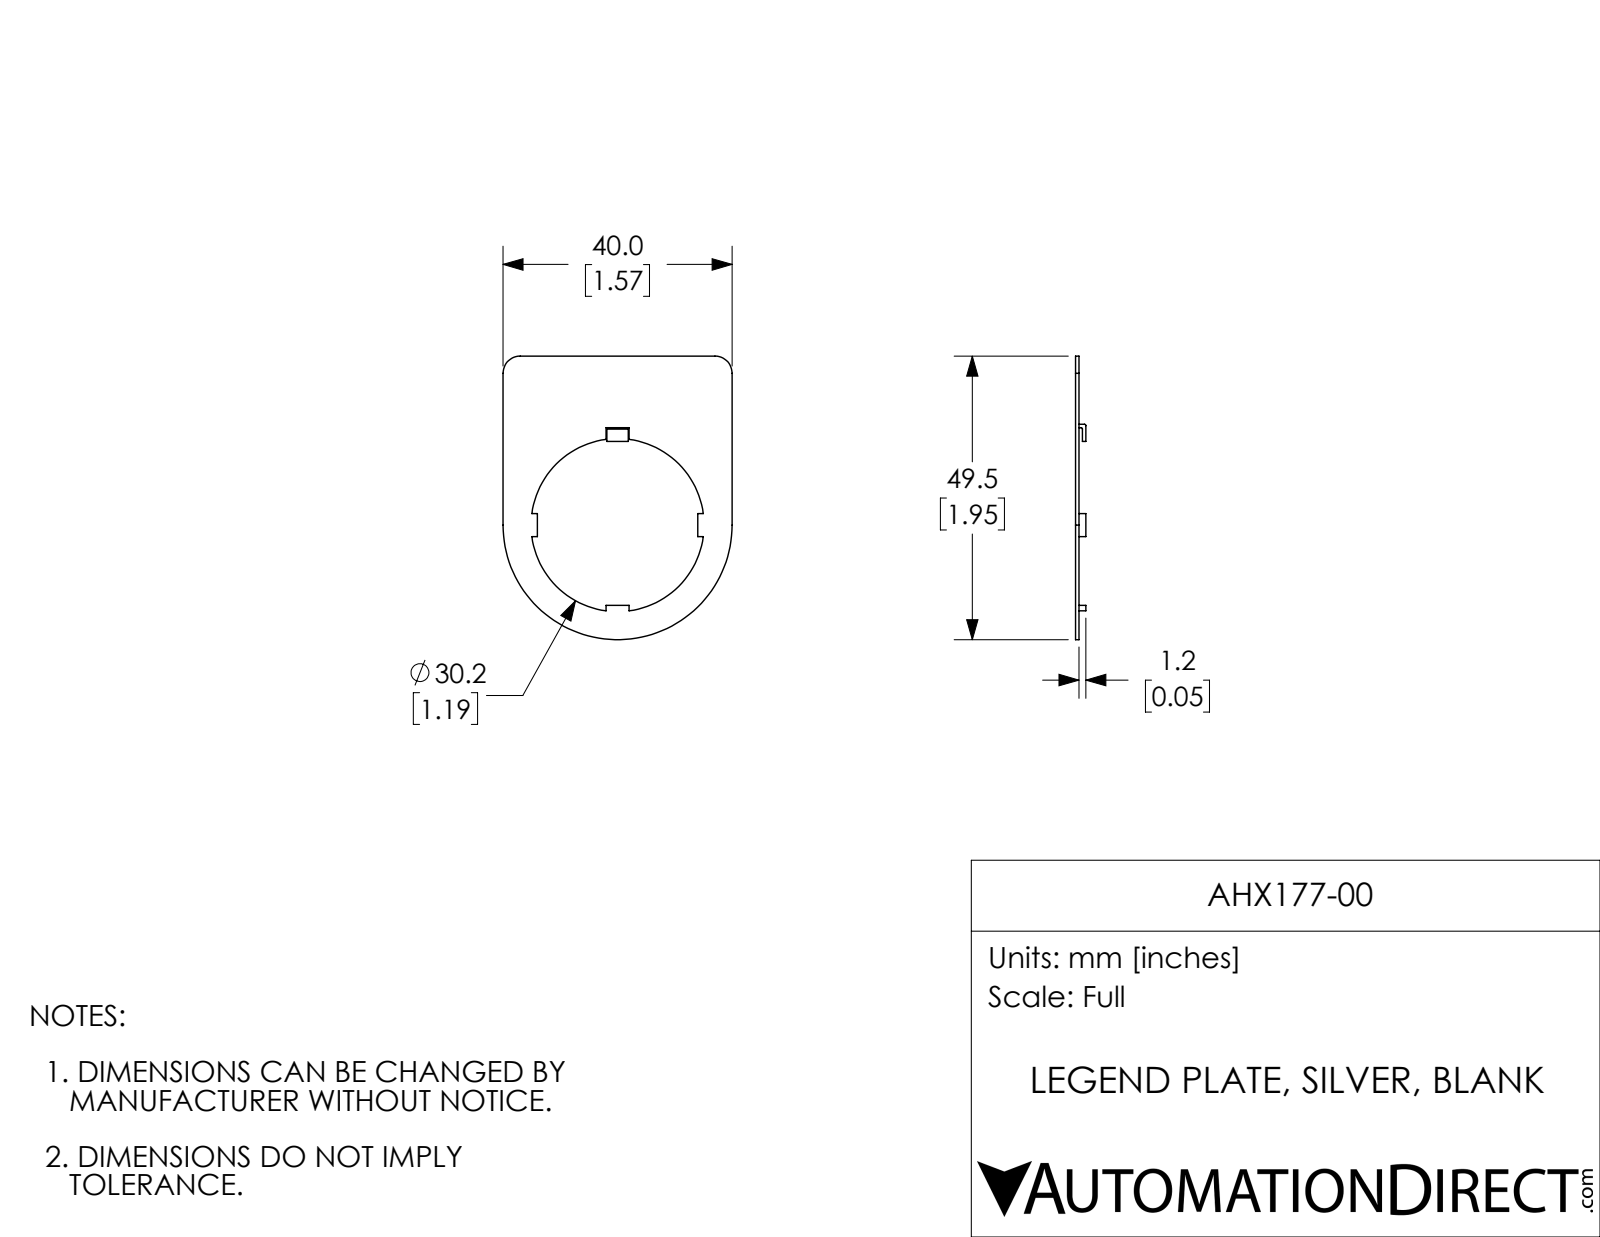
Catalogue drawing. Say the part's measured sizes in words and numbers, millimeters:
The part is named "AHX177-00". Its 3-D file was written by "SolidWorks 2017 (AUTOMOTIVE_DESIGN)". It is 1 solid with 38 faces: 29 planar, 9 cylindrical and 0 other. Overall it measures 49.5 by 40 by 1.8 millimeters. Its volume is 670 cubic millimeters and its surface area 2 410 square millimeters. Round holes: 1 of diameter 30.2. Partial cylindrical surfaces (rounded edges, fillets, slot ends): 2 of radius 0.3, 2 of radius 3, 1 of radius 20. The main face-to-face distances are 0.6, 1.2, 1.8, 40, 1, 6, 34, 5, 35, 29.
